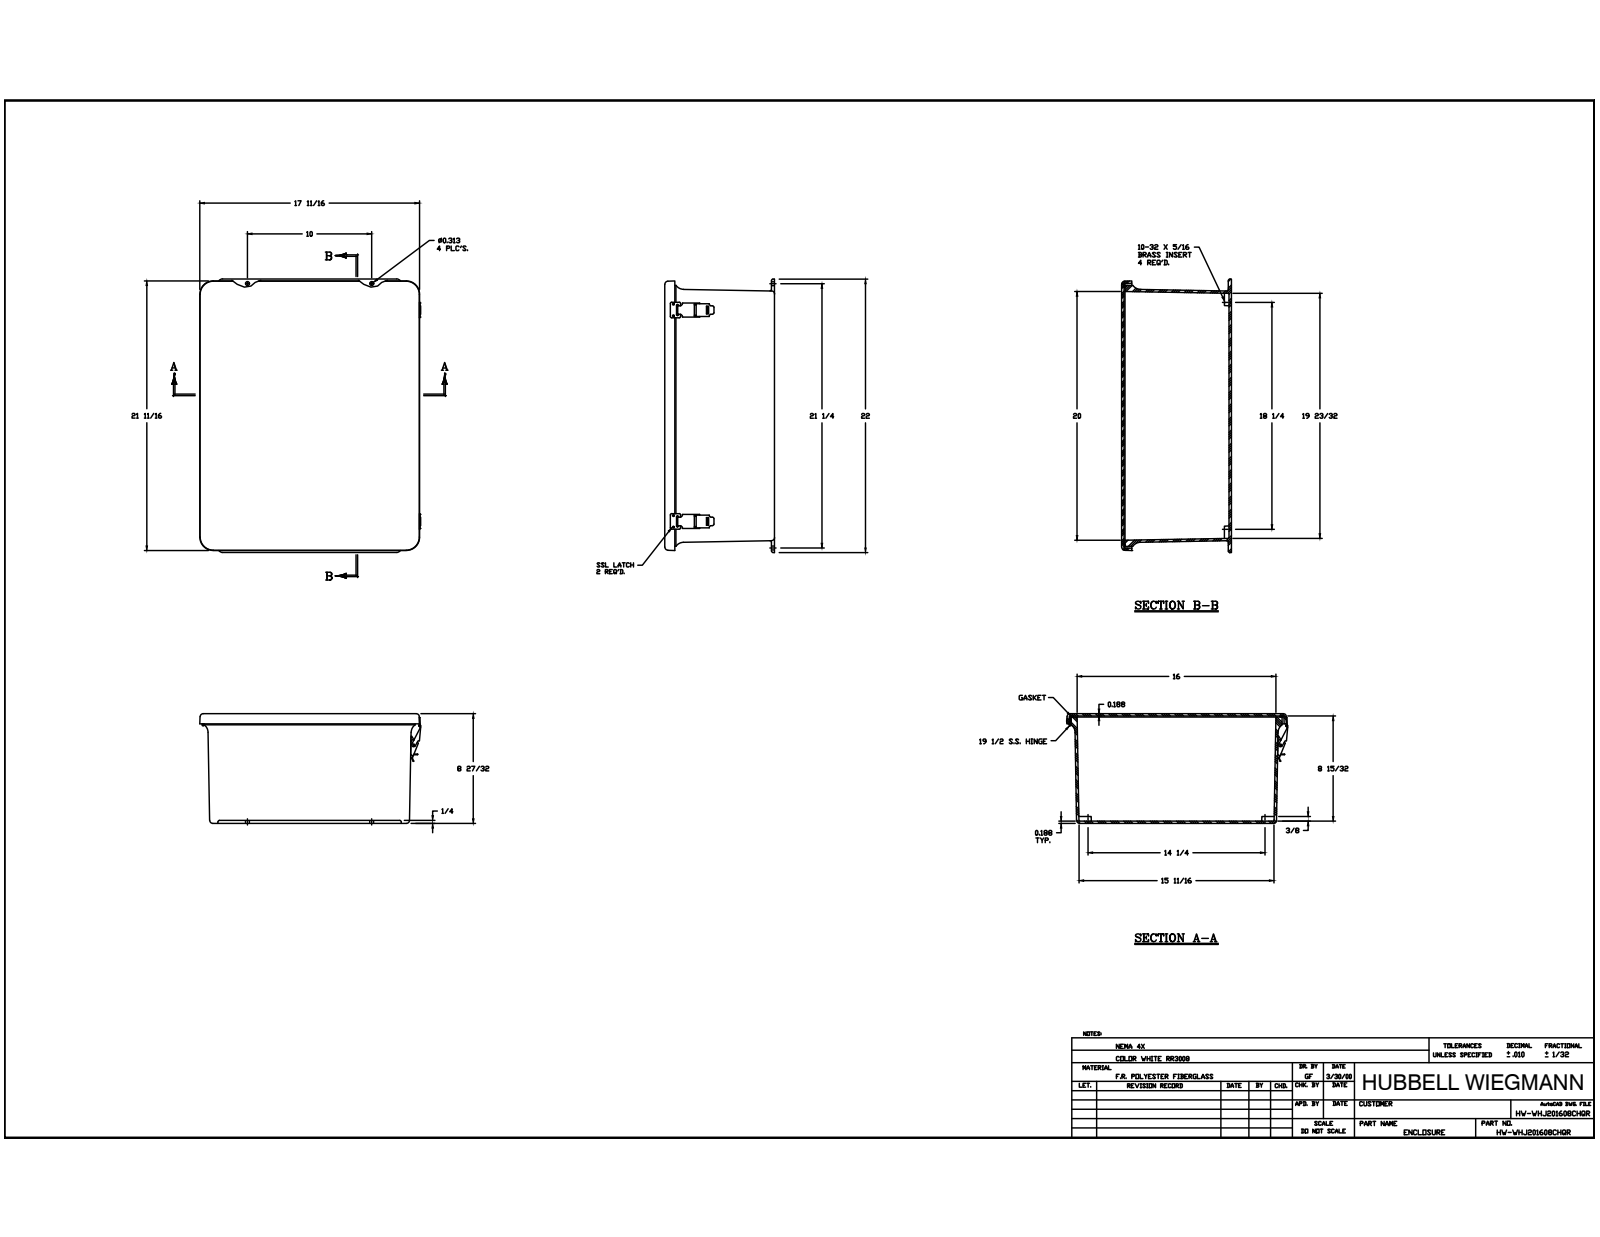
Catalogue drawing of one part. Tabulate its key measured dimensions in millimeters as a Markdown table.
| quantity | value |
| --- | --- |
| part name | J2016HL_2; RMINS45821P_19; RMINS45821P_20; RMINS45821P_21 (+8 more) |
| STEP written by | Autodesk Inventor 2014 (AUTOMOTIVE_DESIGN) |
| units | millimeters |
| bodies | 42 solids, 1165 faces (533 planar, 489 cylindrical, 143 other) |
| overall size | 558.8 × 451.4 × 224.26 |
| volume | 4 647 000 mm³ |
| surface area | 1 917 000 mm² |
| round holes (diameter × count) | 3.56 × 24, 3.33 × 12, 2.64 × 8, 3.86 × 5, 3.3 × 4, 3.96 × 4, 5.54 × 4, 3.43 × 2, 9.52 × 2, 2.16 × 1 |
| round bosses / shafts (diameter × count) | 3.17 × 20, 6.35 × 12, 6.86 × 4, 7.62 × 1, 4.31 × 1, 3.94 × 1, 3.05 × 1 |
| partial cylindrical surfaces (radius × count) | 0.38 × 20, 0.79 × 20, 3.17 × 18, 1.14 × 16, 0.76 × 12, 0.57 × 9, 6.35 × 8, 1.52 × 6 |
| main face-to-face distances | 4.76, 219.5, 224.26, 4.77, 214.73, 219.49, 7.94, 12.7, 217.49, 212.72 |
| hole center spacings | 95.25, 431.8, 190.5, 23.81, 6.35, 88.9, 101.6, 184.15 |
